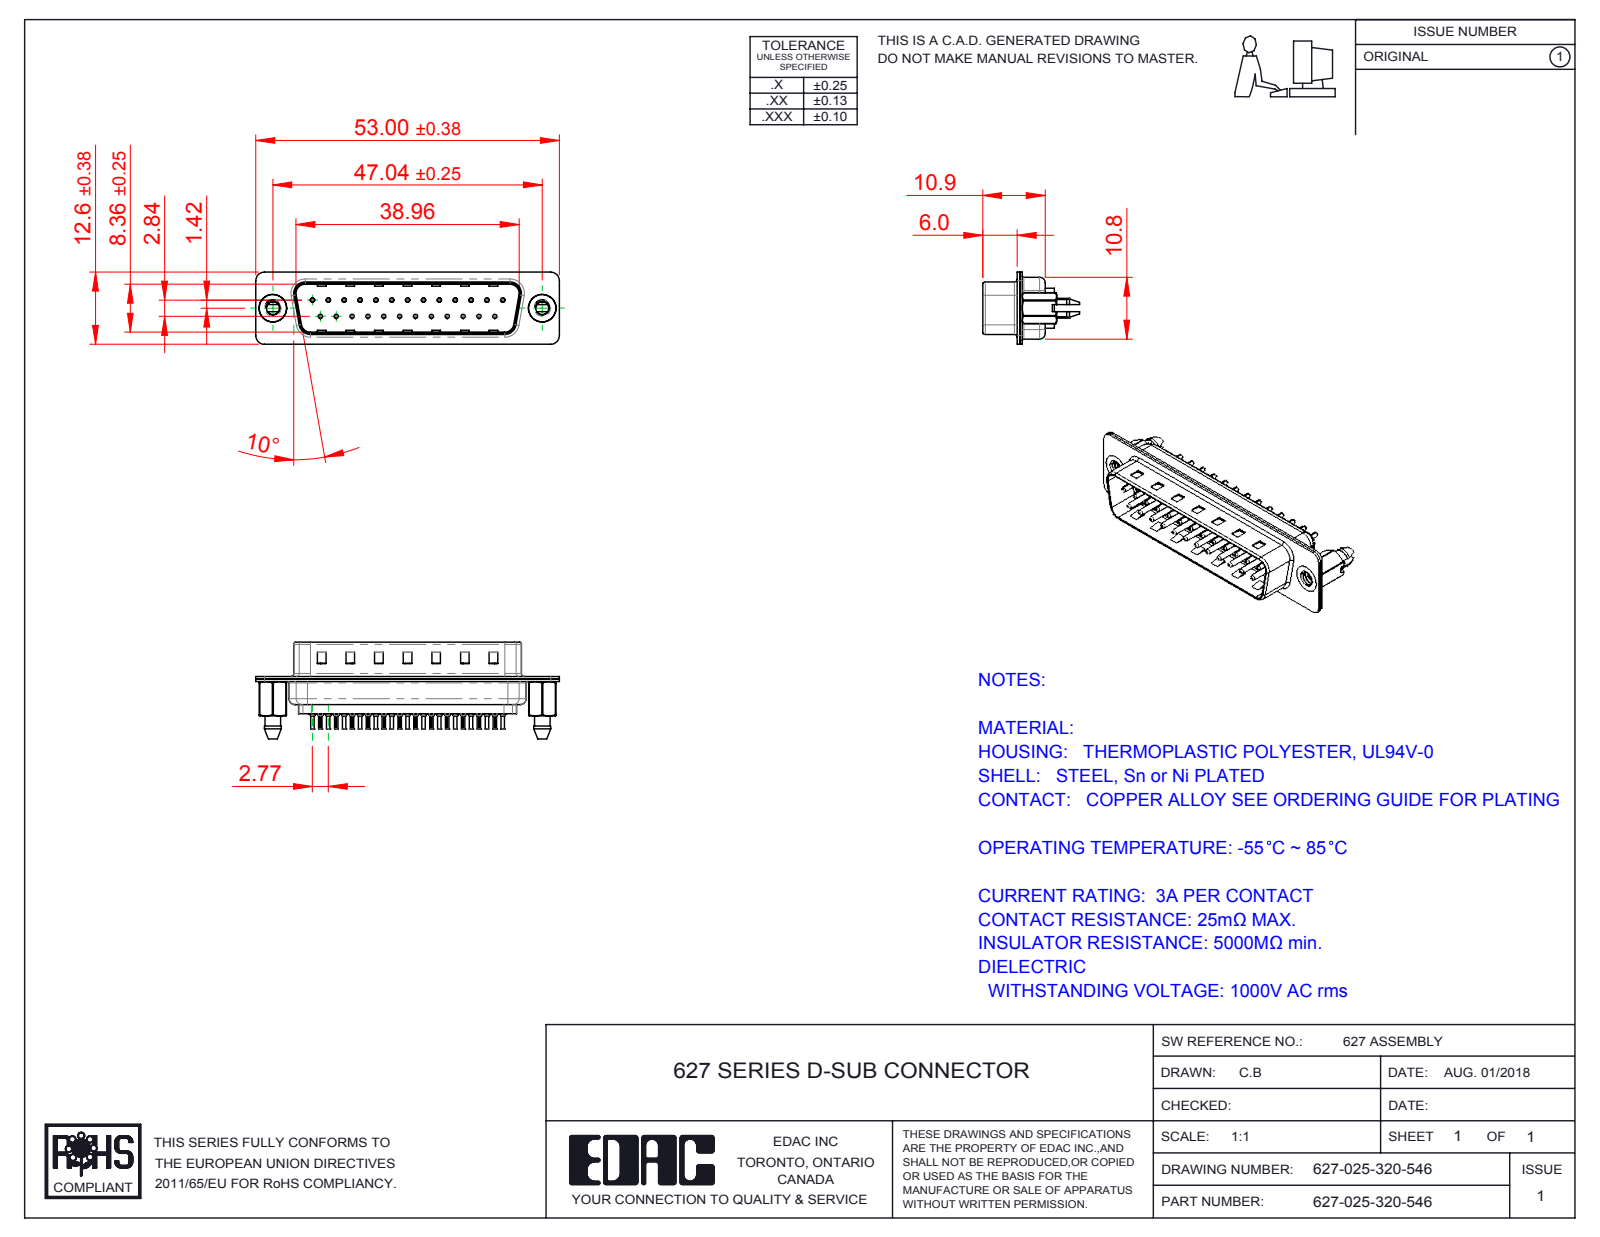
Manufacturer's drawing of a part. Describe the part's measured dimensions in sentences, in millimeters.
The part is named "627 Shell Rear_25 Contacts; 627 Shell Front_25 Contacts; 627 4-40 Threaded Boardlock_LP; 627-025-320-546 (+3 more)". Its 3-D file was written by "SolidWorks 2016 (CONFIG_CONTROL_DESIGN)". It is 30 solids with 2900 faces: 803 planar, 1094 cylindrical and 1003 other. Overall it measures 53 by 16.9 by 12.6 millimeters. Its volume is 2 784 cubic millimeters and its surface area 7 945 square millimeters. Round holes: 25 of diameter 0.2, 25 of diameter 0.35, 25 of diameter 1.1, 25 of diameter 1.6, 2 of diameter 2.26, 2 of diameter 4, 2 of diameter 4.8. Round bosses or shafts: 25 of diameter 2, 25 of diameter 1.5, 25 of diameter 0.75, 25 of diameter 0.6, 2 of diameter 4.9. Partial cylindrical surfaces (rounded edges, fillets, slot ends): 50 of radius 0.1, 18 of radius 1.5, 12 of radius 2, 10 of radius 1.6, 8 of radius 0.5, 4 of radius 0.25, 4 of radius 0.6, 4 of radius 0.65. The main face-to-face distances are 0.4, 0.45, 0.82, 9.58, 8.76, 0.9, 1.5, 1.4, 6.5, 6.05. The hole center spacings are 3.16, 8.31, 2.77, 5.54, 11.08, 16.62, 5.03, 5.04.
